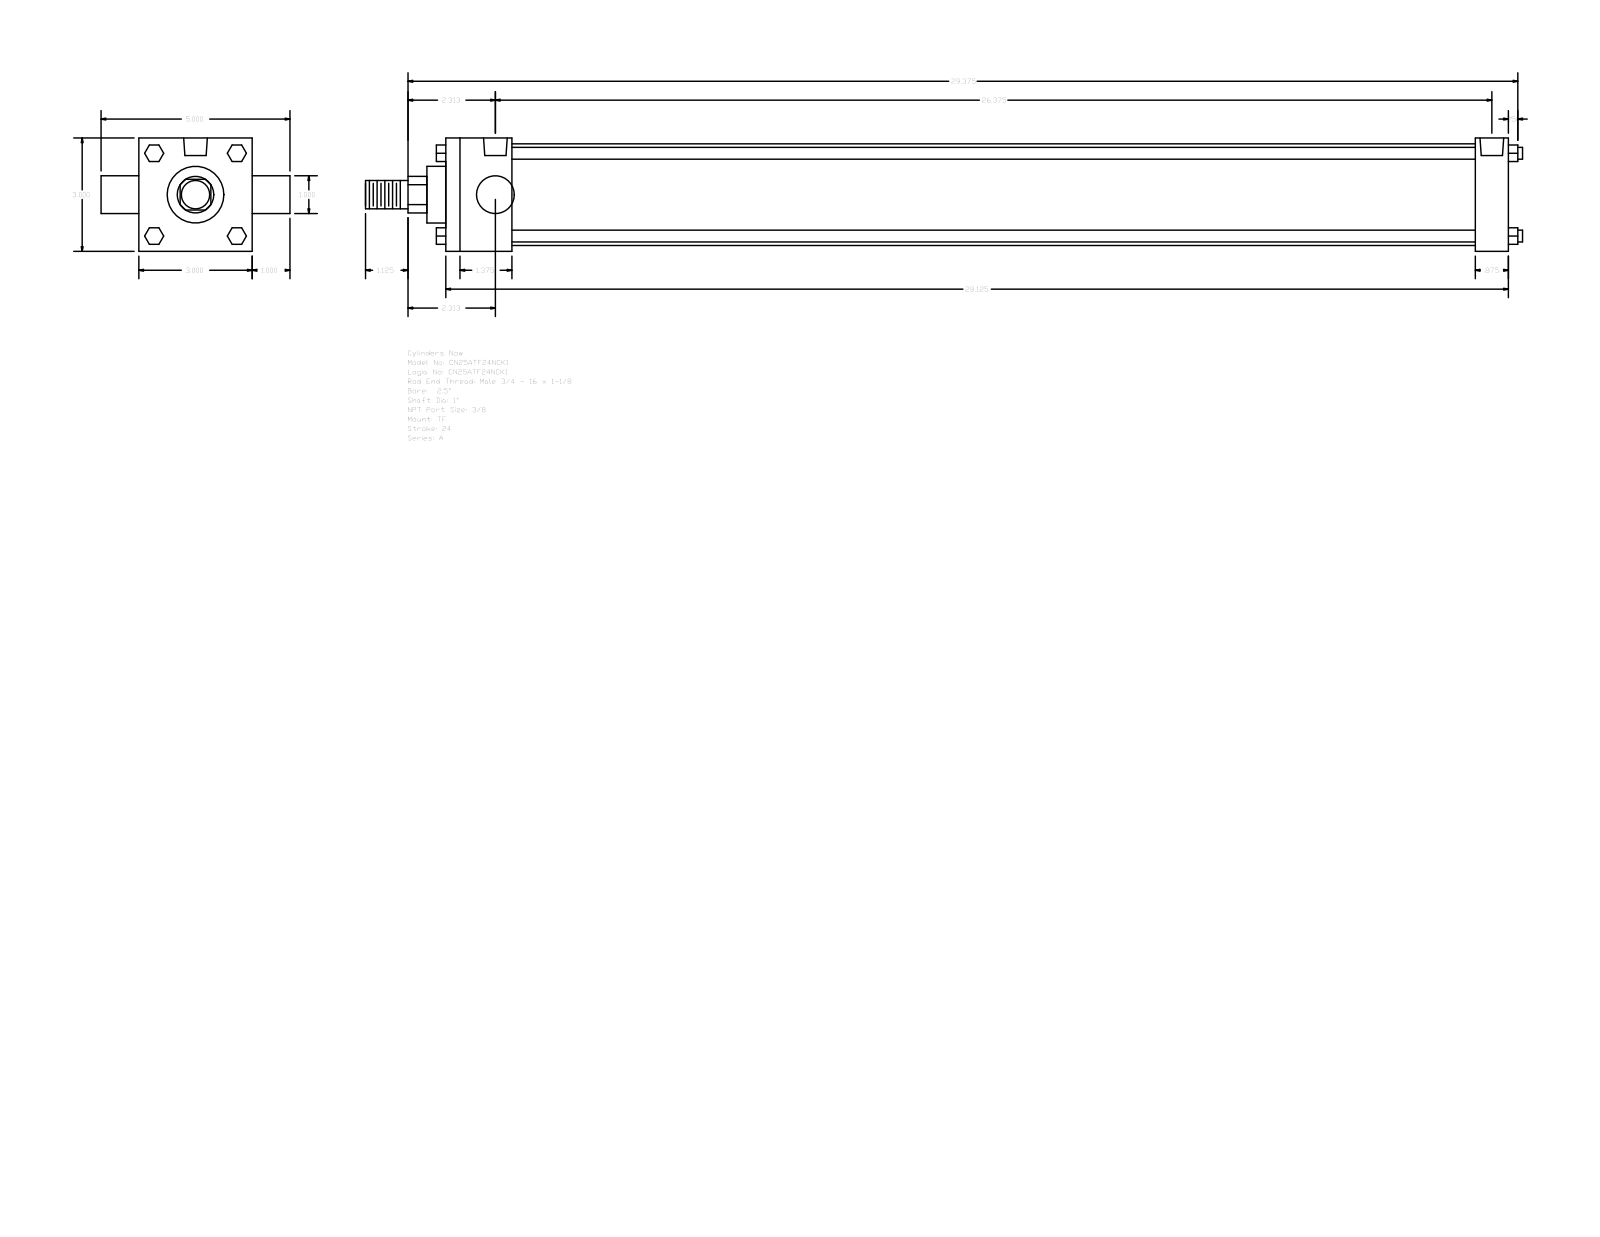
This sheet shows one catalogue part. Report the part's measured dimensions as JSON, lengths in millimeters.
{"part_name": "A_TF__0250_1", "step_written_by": "GSSL Pune (CONFIG_CONTROL_DESIGN)", "units": "millimeters", "bodies": {"solids": 0, "faces": 120, "planar": 92, "cylindrical": 28, "other": 0}, "overall_size": [777.88, 127, 76.2], "round_holes": [[5.56, 3], [15.93, 2]], "round_bosses_or_shafts": [[7.94, 4], [25.4, 2], [68.33, 1], [38.1, 1], [19.05, 1]], "partial_cylinders_radius": [[12.29, 1]], "face_to_face_distances": [76.2, 714.37, 44.45, 692.15, 647.7, 669.92, 22.22, 25.4, 101.6, 727.07], "hole_center_spacings": [2.38, 672.3, 669.92, 674.68]}
